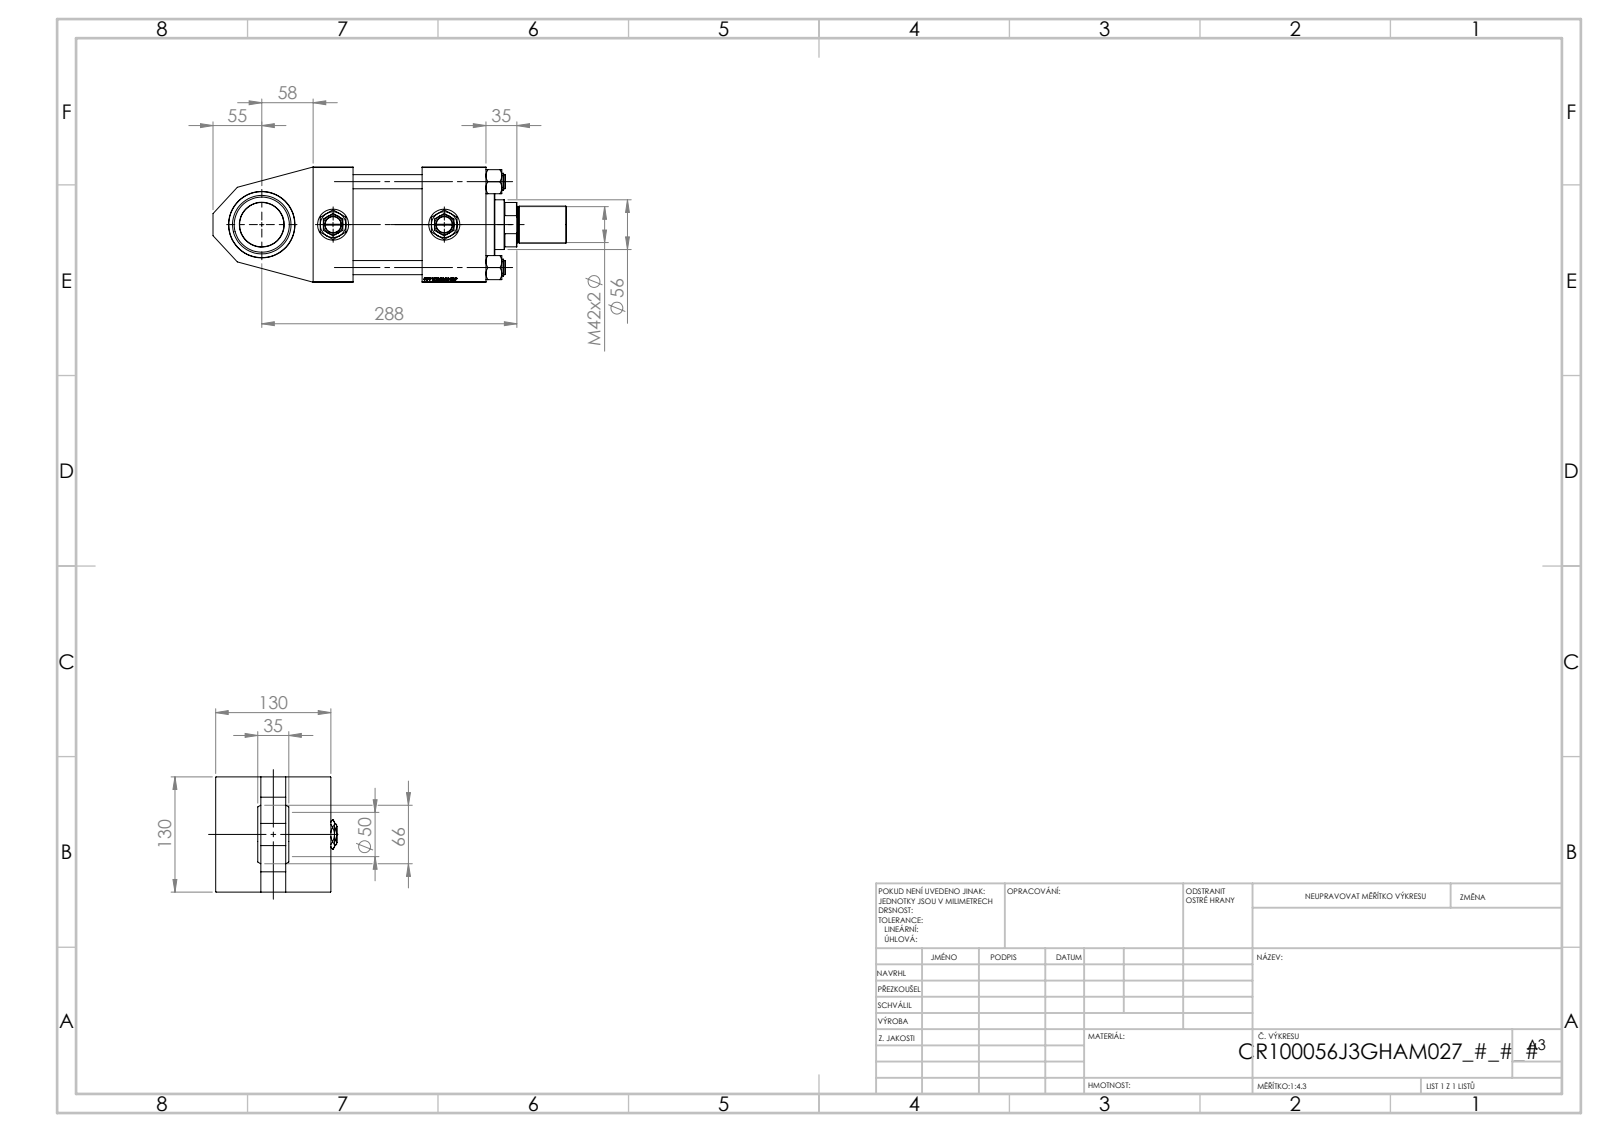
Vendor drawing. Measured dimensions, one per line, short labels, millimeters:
name: Zatka_pro_OIL_PORT; V215CR_TYCINKA_J; V215CR_J_VNITRNI_KROUZEK; V215CR_VCP_J (+4 more)
written by: SolidWorks 2019 (CONFIG_CONTROL_DESIGN)
unit: mm
bodies: 15 solids, 1308 faces (616 planar, 104 cylindrical, 588 other)
size: 399 × 137 × 130
volume: 2 844 000 mm³; area: 403 834 mm²
holes: 4× ⌀16, 2× ⌀2.5, 2× ⌀7, 2× ⌀26.44, 2× ⌀35, 1× ⌀40.5, 1× ⌀50, 1× ⌀56, 1× ⌀59, 1× ⌀75, 1× ⌀76, 1× ⌀85.5
bosses: 4× ⌀19, 1× ⌀106, 1× ⌀72, 1× ⌀42, 1× ⌀40
rounds: 1× R27
face distances: 130, 51, 79, 45, 150, 195, 123, 78, 72, 28
hole spacings: 49.02, 68.52, 96.9, 101.73, 41, 137.04, 80.5, 82
